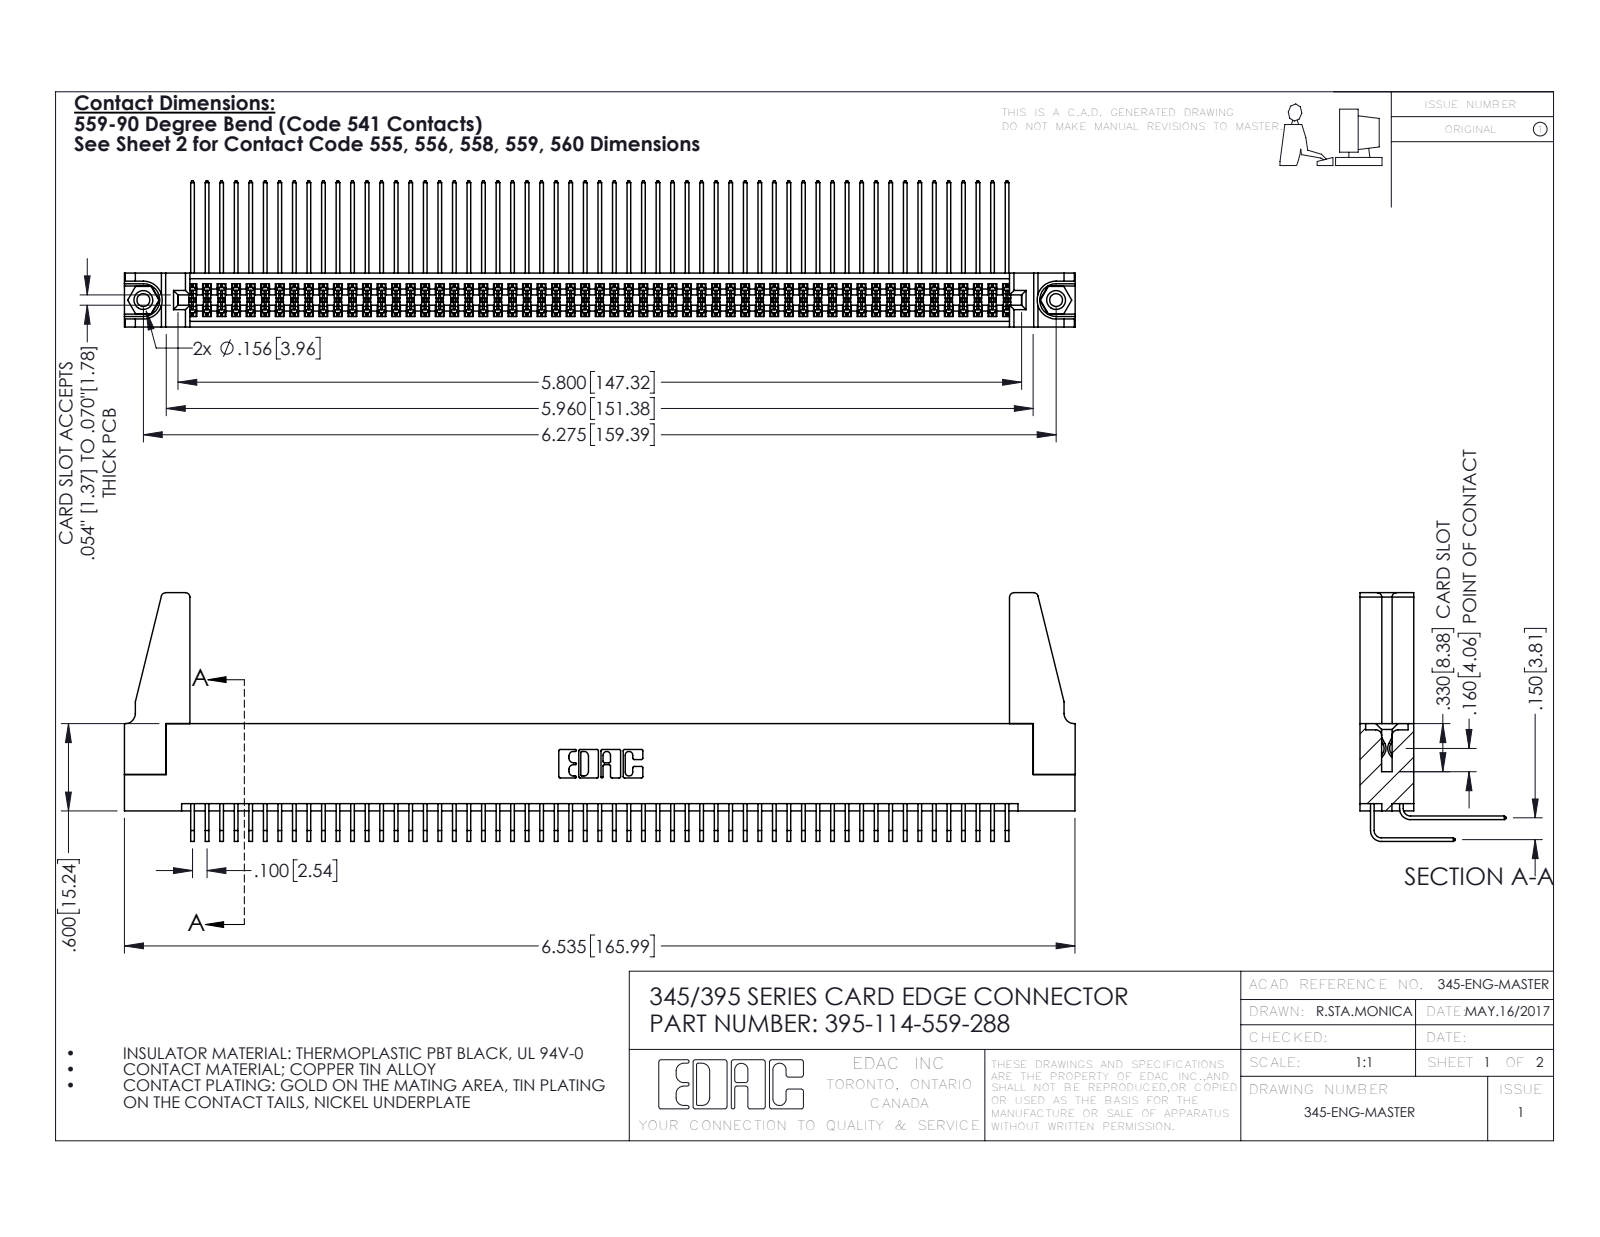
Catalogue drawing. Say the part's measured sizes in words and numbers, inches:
The part is named "345-292-001_558 559 Tail - 1; 345 Part_Flush Mounting Lugs - 0.156 Dia-TH; 395-114-559-288; 345-292-001_559 Tail - 2 (+2 more)". Its 3-D file was written by "SolidWorks 2016 (CONFIG_CONTROL_DESIGN)". It is 119 solids with 6178 faces: 4142 planar, 2020 cylindrical and 16 other. Overall it measures 6.536 by 1.709 by 1.005 inches. Its volume is 1.231 cubic inches and its surface area 48.86 square inches. Round holes: 2 of diameter 0.089, 2 of diameter 0.125, 2 of diameter 0.156, 1 of diameter 0.064. Round bosses or shafts: 2 of diameter 0.155. Partial cylindrical surfaces (rounded edges, fillets, slot ends): 171 of radius 0.006, 22 of radius 0.01, 8 of radius 0.03, 6 of radius 0.007, 6 of radius 0.031, 3 of radius 0.026, 2 of radius 0.014, 2 of radius 0.019. The main face-to-face distances are 0.072, 0.298, 0.37, 0.2, 0.098, 0.272, 0.025, 0.225, 0.175, 0.15. The hole center spacings are 0.27, 6.039, 6.275.
